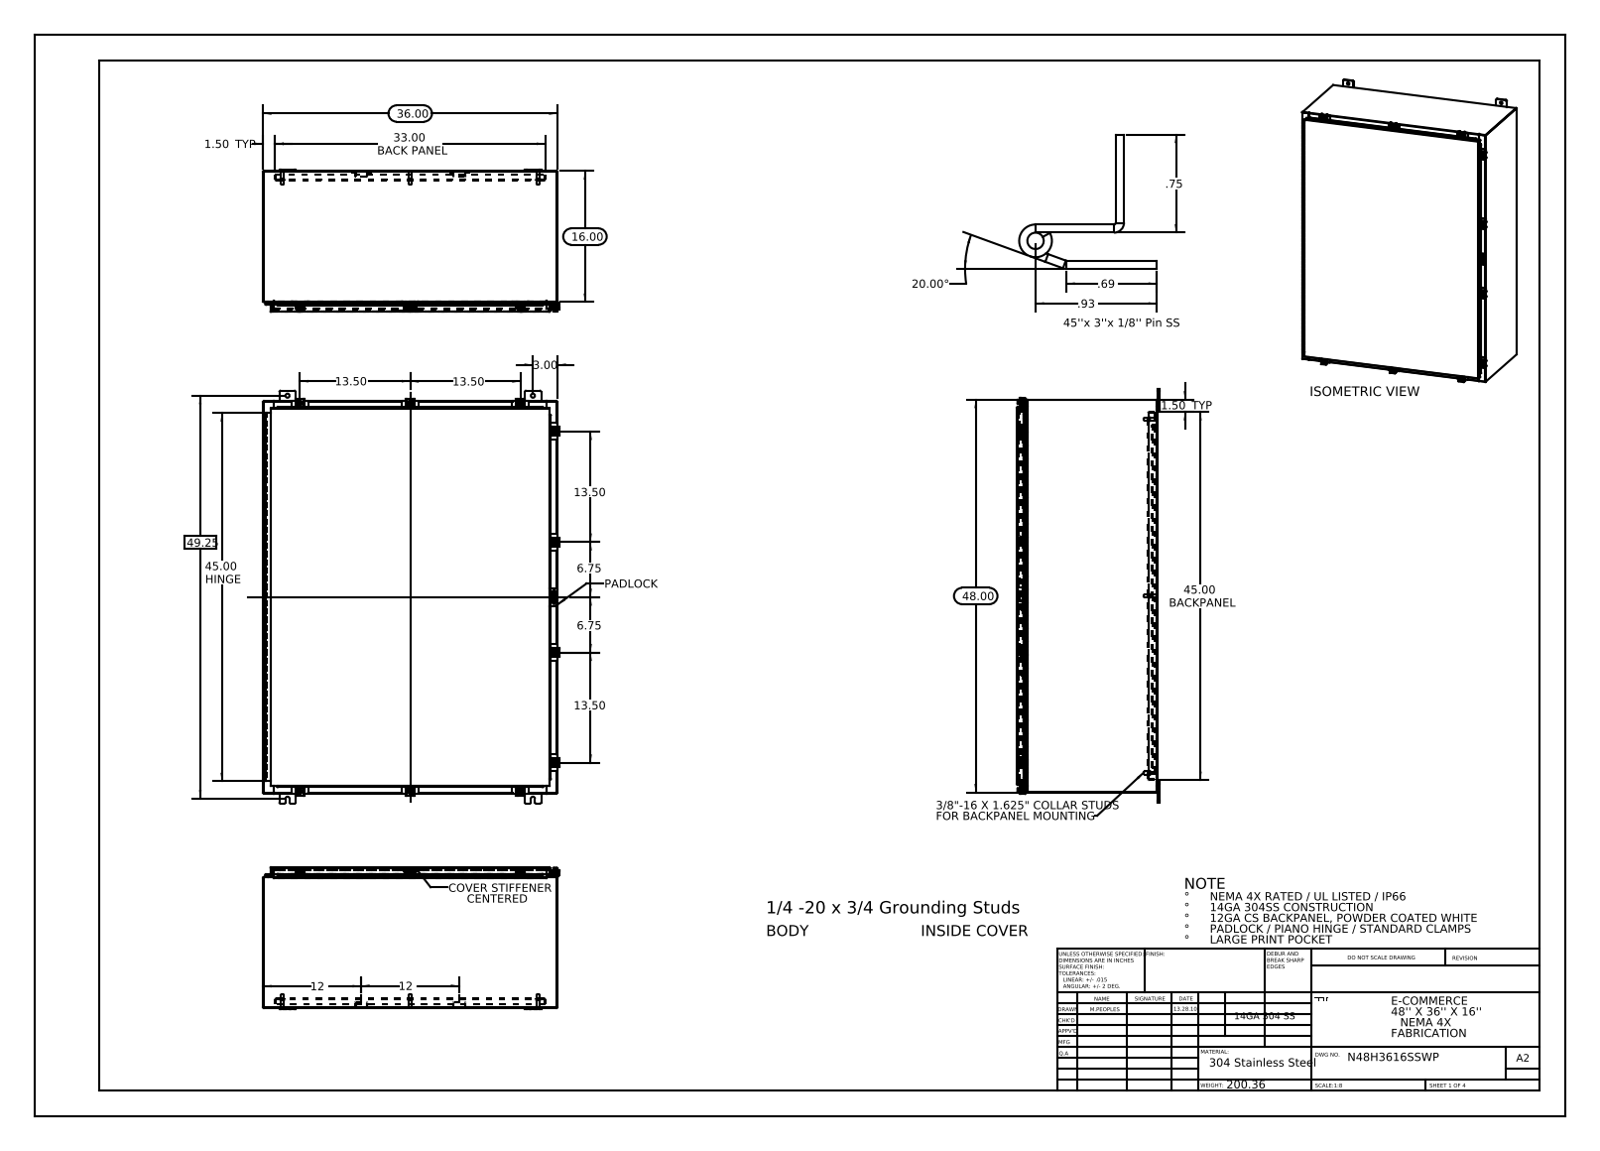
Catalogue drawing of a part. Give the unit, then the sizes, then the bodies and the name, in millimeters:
Units: millimetres
Overall size (bounding box): 1282.7 × 919.8 × 441.7
Round holes (diameter × count): ⌀12.7 ×12, ⌀5.4 ×10, ⌀6.6 ×10, ⌀6.4 ×6, ⌀3.2 ×2, ⌀3.2 ×1
Round bosses / shafts (diameter × count): ⌀6.4 ×11, ⌀12.7 ×10, ⌀10.1 ×10, ⌀15.9 ×8, ⌀9.5 ×8, ⌀8.4 ×8
Partial cylindrical surfaces — rounded edges, fillets, slot ends (radius × count): R1.5 ×46, R0.3 ×39, R2.2 ×33, R4.8 ×24, R3 ×20, R3.6 ×20, R1.3 ×15, R2 ×14
Main face-to-face distances: 1.9, 435, 433.1, 2.6, 436.9, 912.5, 25.4, 409.6, 27.3, 407.7
Hole centre spacings: 342.9, 347, 508, 511.1, 549.3, 605, 685.8, 965.3
Volume: 11 480 000 mm³ · Surface area: 11 350 000 mm²
Bodies: 74 solids, 2999 faces (1562 planar, 1269 cylindrical, 168 other)
Part name (STEP PRODUCT): N48H3616SSWP Mounting Feet; N48H3616SSWP Clamp Assembly; N48H3616SSWP 125 Pin Hinge; N48H3616SSWP Enclosure Stiffener (+8 more)
STEP written by: SolidWorks 2013 (CONFIG_CONTROL_DESIGN)
